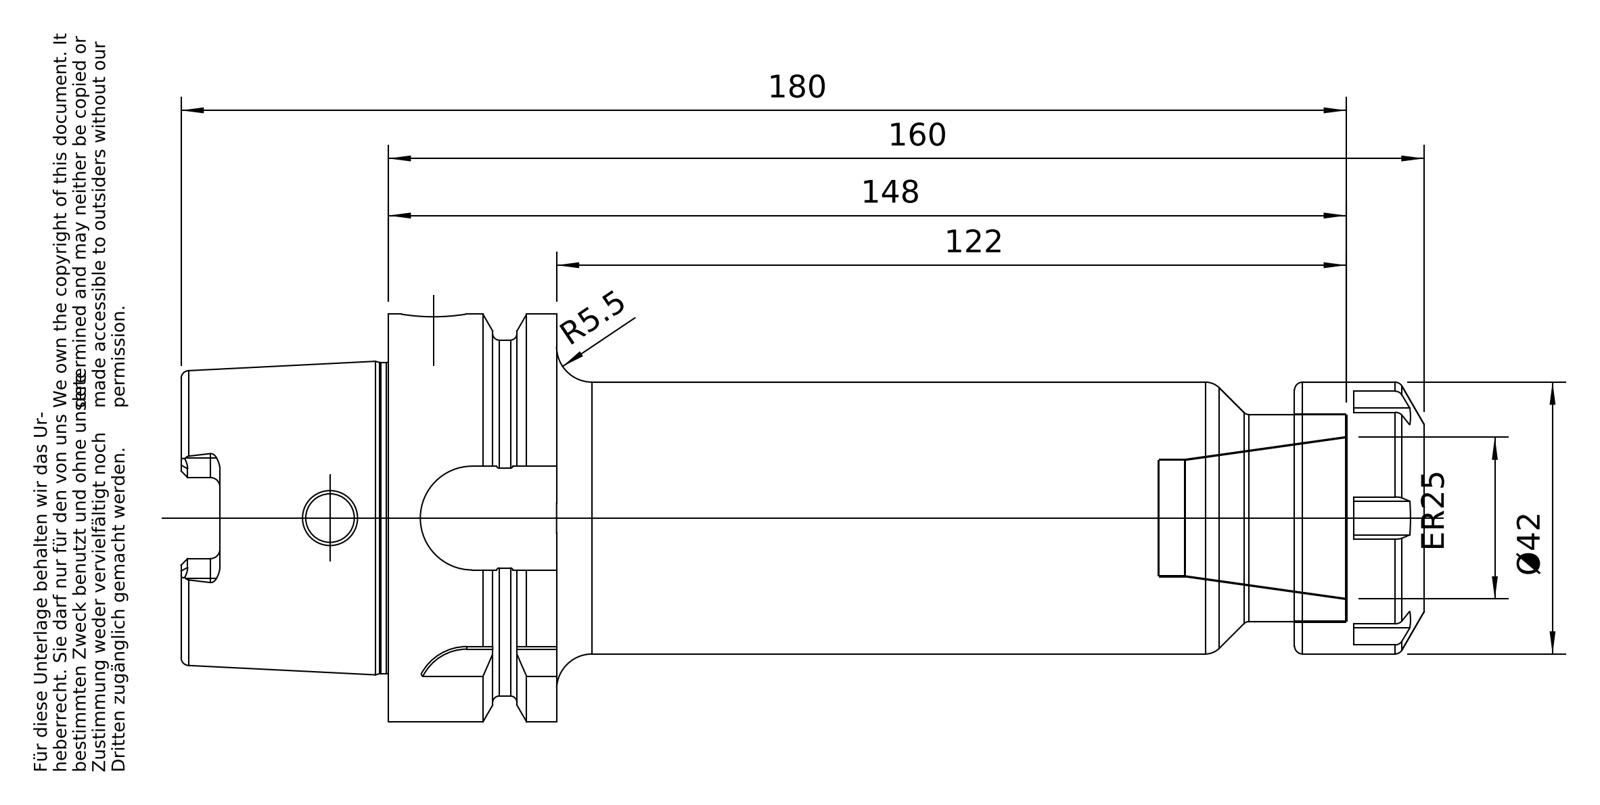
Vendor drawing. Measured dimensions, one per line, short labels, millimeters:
name: A63-022-25; 83-912-25; A63-022-25_ASM
written by: PRO/ENGINEER BY PARAMETRIC TECHNOLOGY CORPORATION, 2010430 (CONFIG_CONTROL_DESIGN)
unit: mm
bodies: 2 solids, 224 faces (78 planar, 52 cylindrical, 94 other)
size: 192 × 63 × 63
volume: 256 597 mm³; area: 44 291 mm²
holes: 1× ⌀7.5, 1× ⌀10, 1× ⌀16.92, 1× ⌀18, 1× ⌀18.32, 1× ⌀18.66, 1× ⌀34, 1× ⌀40
bosses: 1× ⌀63, 1× ⌀55, 1× ⌀48.04, 1× ⌀42, 1× ⌀32
rounds: 6× R1.5, 4× R3, 1× R8, 1× R8.02, 1× R9.02
face distances: 140, 26, 114, 160, 134, 20, 10, 16, 130, 150
